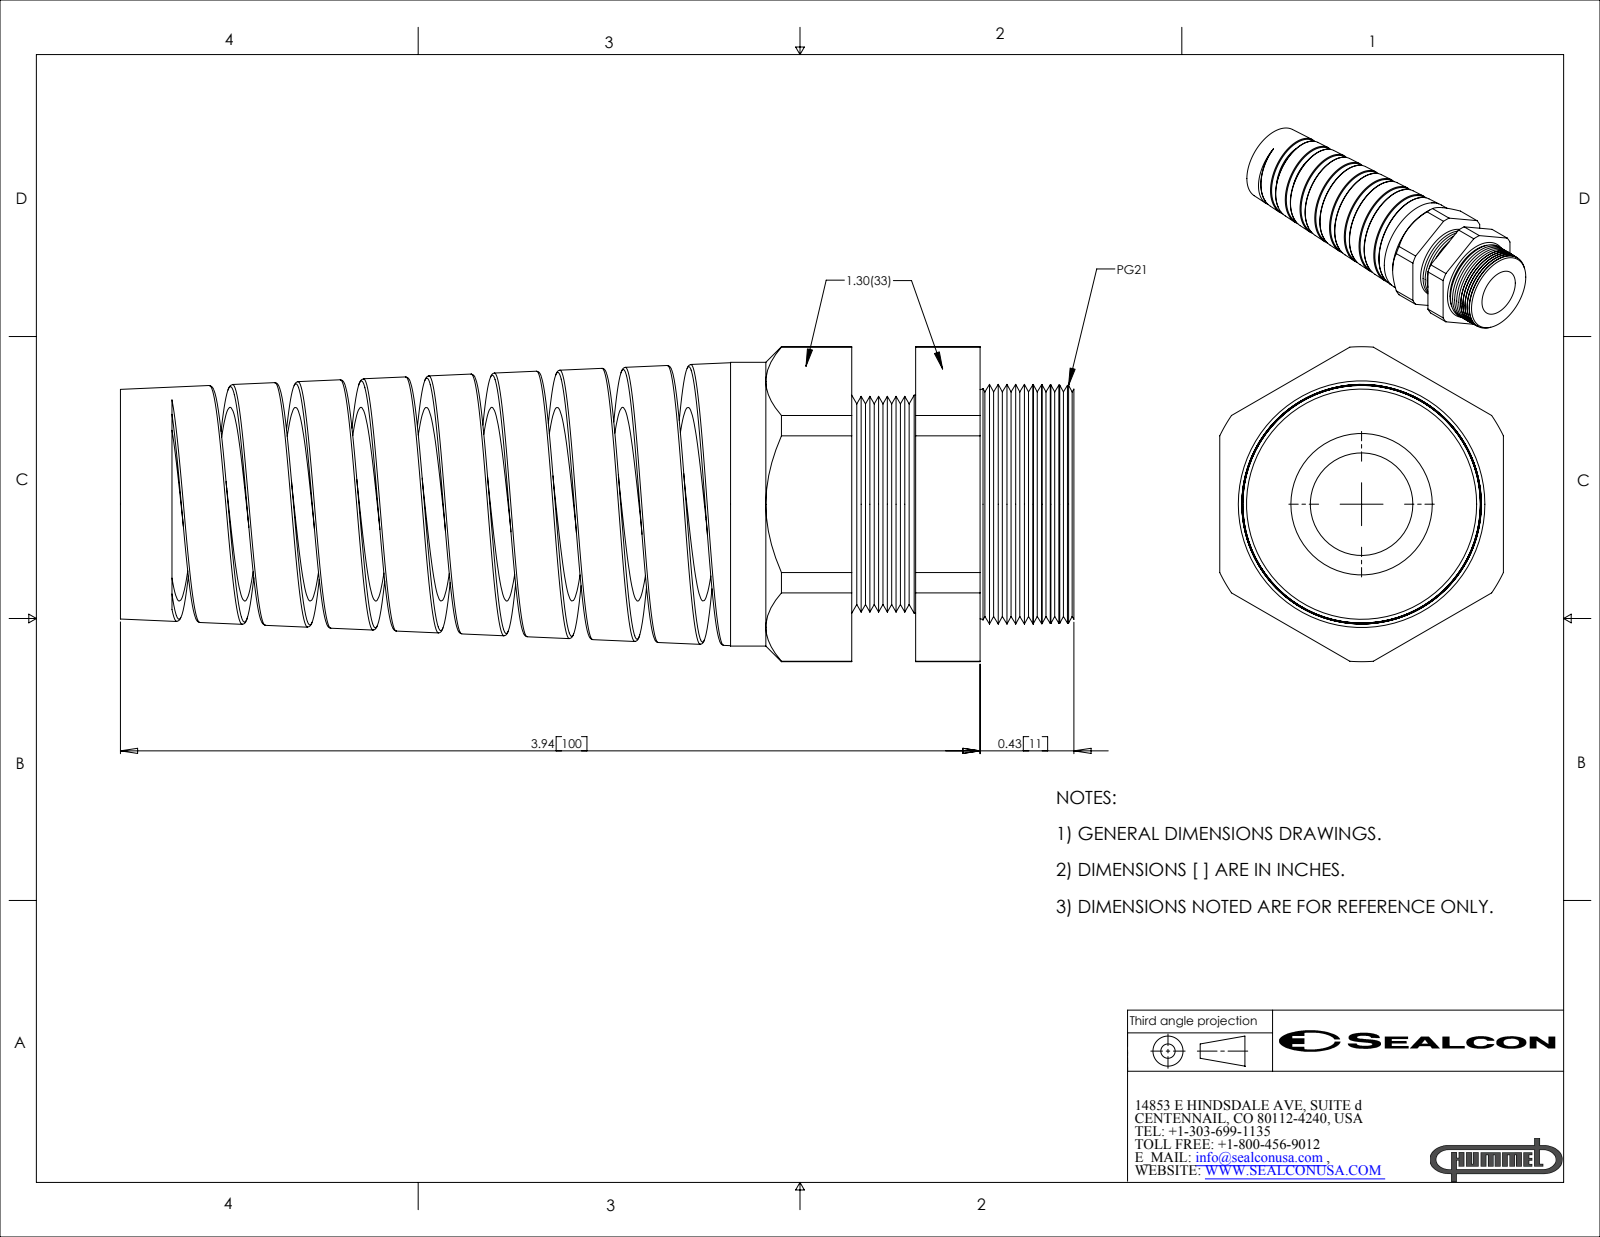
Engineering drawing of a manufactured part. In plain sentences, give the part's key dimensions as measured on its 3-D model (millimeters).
The part is named "CF21BR-BK". Its 3-D file was written by "SolidWorks 2007 (CONFIG_CONTROL_DESIGN)". It is 2 solids with 188 faces: 24 planar, 43 cylindrical and 121 other. Overall it measures 111 by 36.7 by 33 millimeters. Its volume is 39 250 cubic millimeters and its surface area 25 440 square millimeters. Round holes: 1 of diameter 11.9, 1 of diameter 22.6. Round bosses or shafts: 1 of diameter 33, 1 of diameter 25.4. Partial cylindrical surfaces (rounded edges, fillets, slot ends): 1 of radius 11.5, 1 of radius 18.3. The main face-to-face distances are 33, 7.4, 25.9, 18.4, 14.9, 7.5, 10.9, 12.2, 19.7, 27.2.
